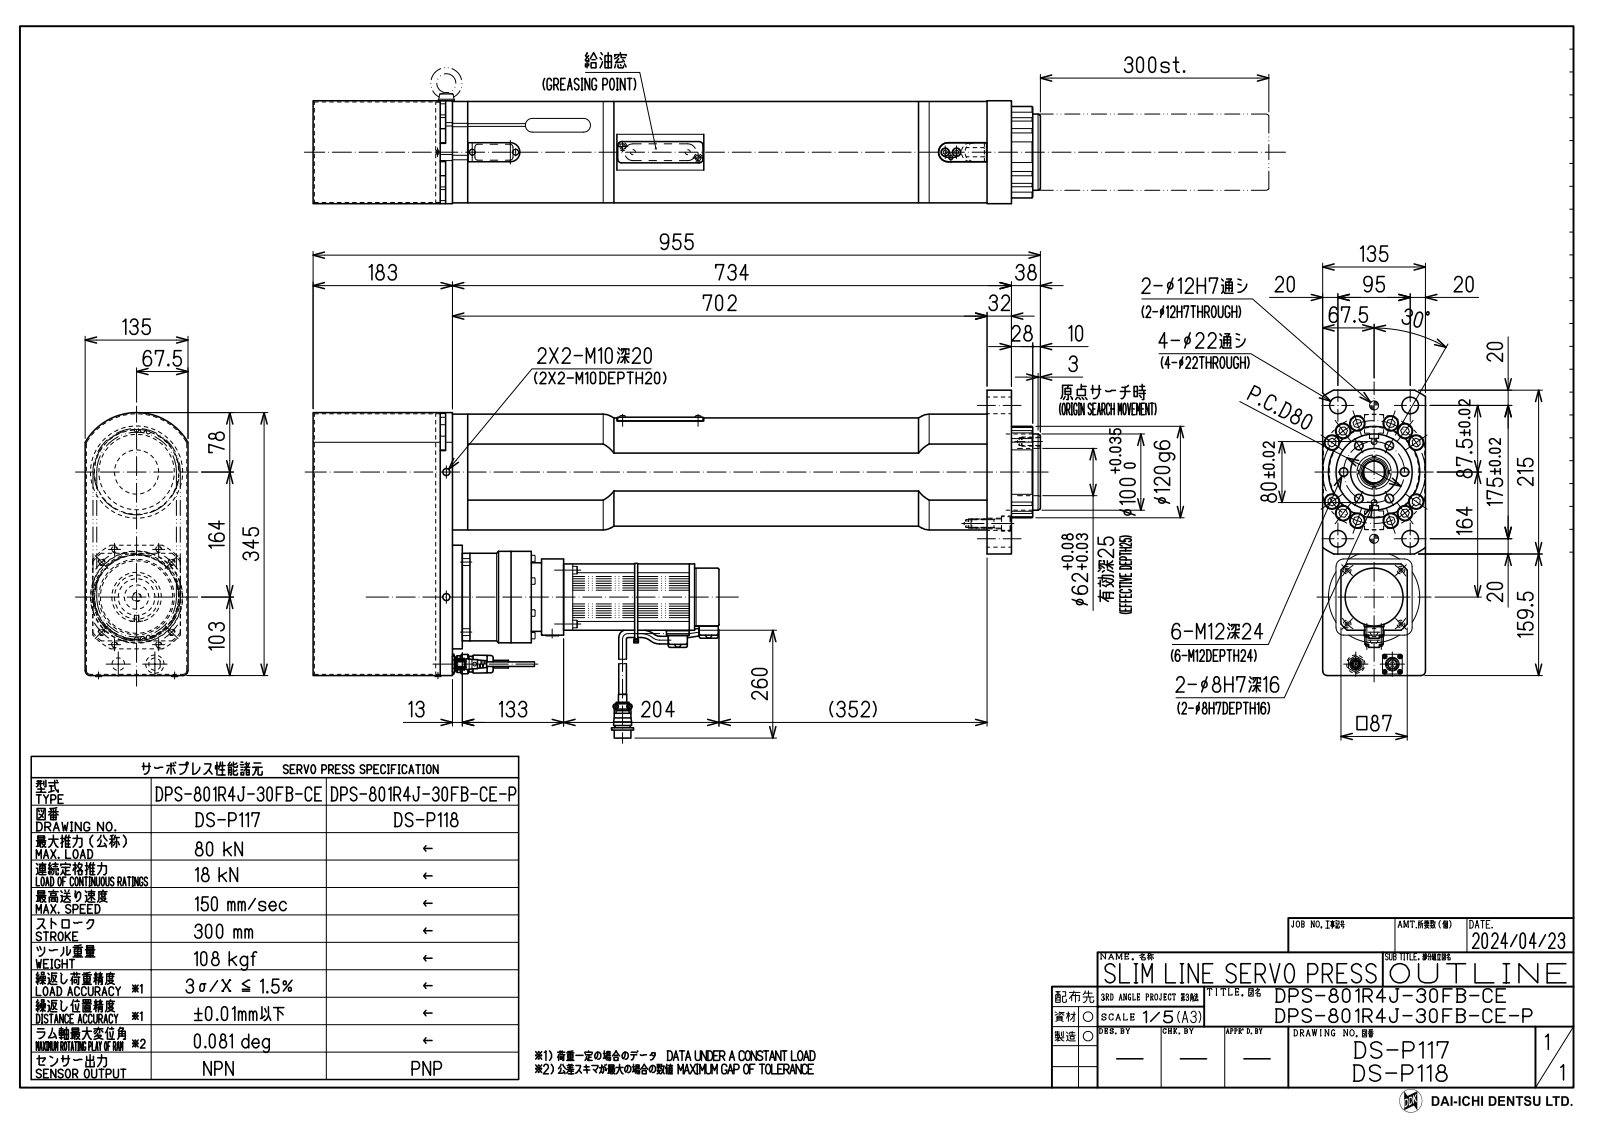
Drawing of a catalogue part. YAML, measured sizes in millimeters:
part_name: "DPS-801R4J-30FB-CE(-P)(DS-P117_P118)_OUTLINE; DPS-801R4J-30FB-CE(DS-P117)_BODY; DPS-102(300st)_SHAFT"
step_written_by: "Autodesk Inventor 2023 (CONFIG_CONTROL_DESIGN)"
units: millimeters
bodies: {solids: 2, faces: 1708, planar: 901, cylindrical: 424, other: 383}
overall_size: [956.5, 376, 135]
volume: 22450000
surface_area: 1222000
round_holes:
  - {diameter: 1, count: 8}
  - {diameter: 4.92, count: 8}
  - {diameter: 6.65, count: 8}
  - {diameter: 1.1, count: 7}
  - {diameter: 10.11, count: 6}
  - {diameter: 1.2, count: 4}
  - {diameter: 3.24, count: 4}
  - {diameter: 4.5, count: 4}
  - {diameter: 6.5, count: 4}
  - {diameter: 8, count: 4}
  - {diameter: 9, count: 4}
  - {diameter: 11, count: 4}
round_bosses_or_shafts:
  - {diameter: 8, count: 11}
  - {diameter: 1.6, count: 8}
  - {diameter: 18, count: 7}
  - {diameter: 1.55, count: 7}
  - {diameter: 1, count: 7}
  - {diameter: 8.5, count: 4}
  - {diameter: 7.5, count: 4}
  - {diameter: 7, count: 4}
partial_cylinders:
  - {radius: 0.6, count: 48}
  - {radius: 1, count: 27}
  - {radius: 3, count: 13}
  - {radius: 2, count: 12}
  - {radius: 5, count: 11}
  - {radius: 10, count: 10}
  - {radius: 2.5, count: 9}
  - {radius: 4, count: 9}
face_to_face_distances: [134, 1, 135, 133, 3, 23, 1.5, 32, 917, 24]
hole_center_spacings: [3, 82.01, 5.2, 10.26, 14.99, 23.69, 27.88, 47.5]
